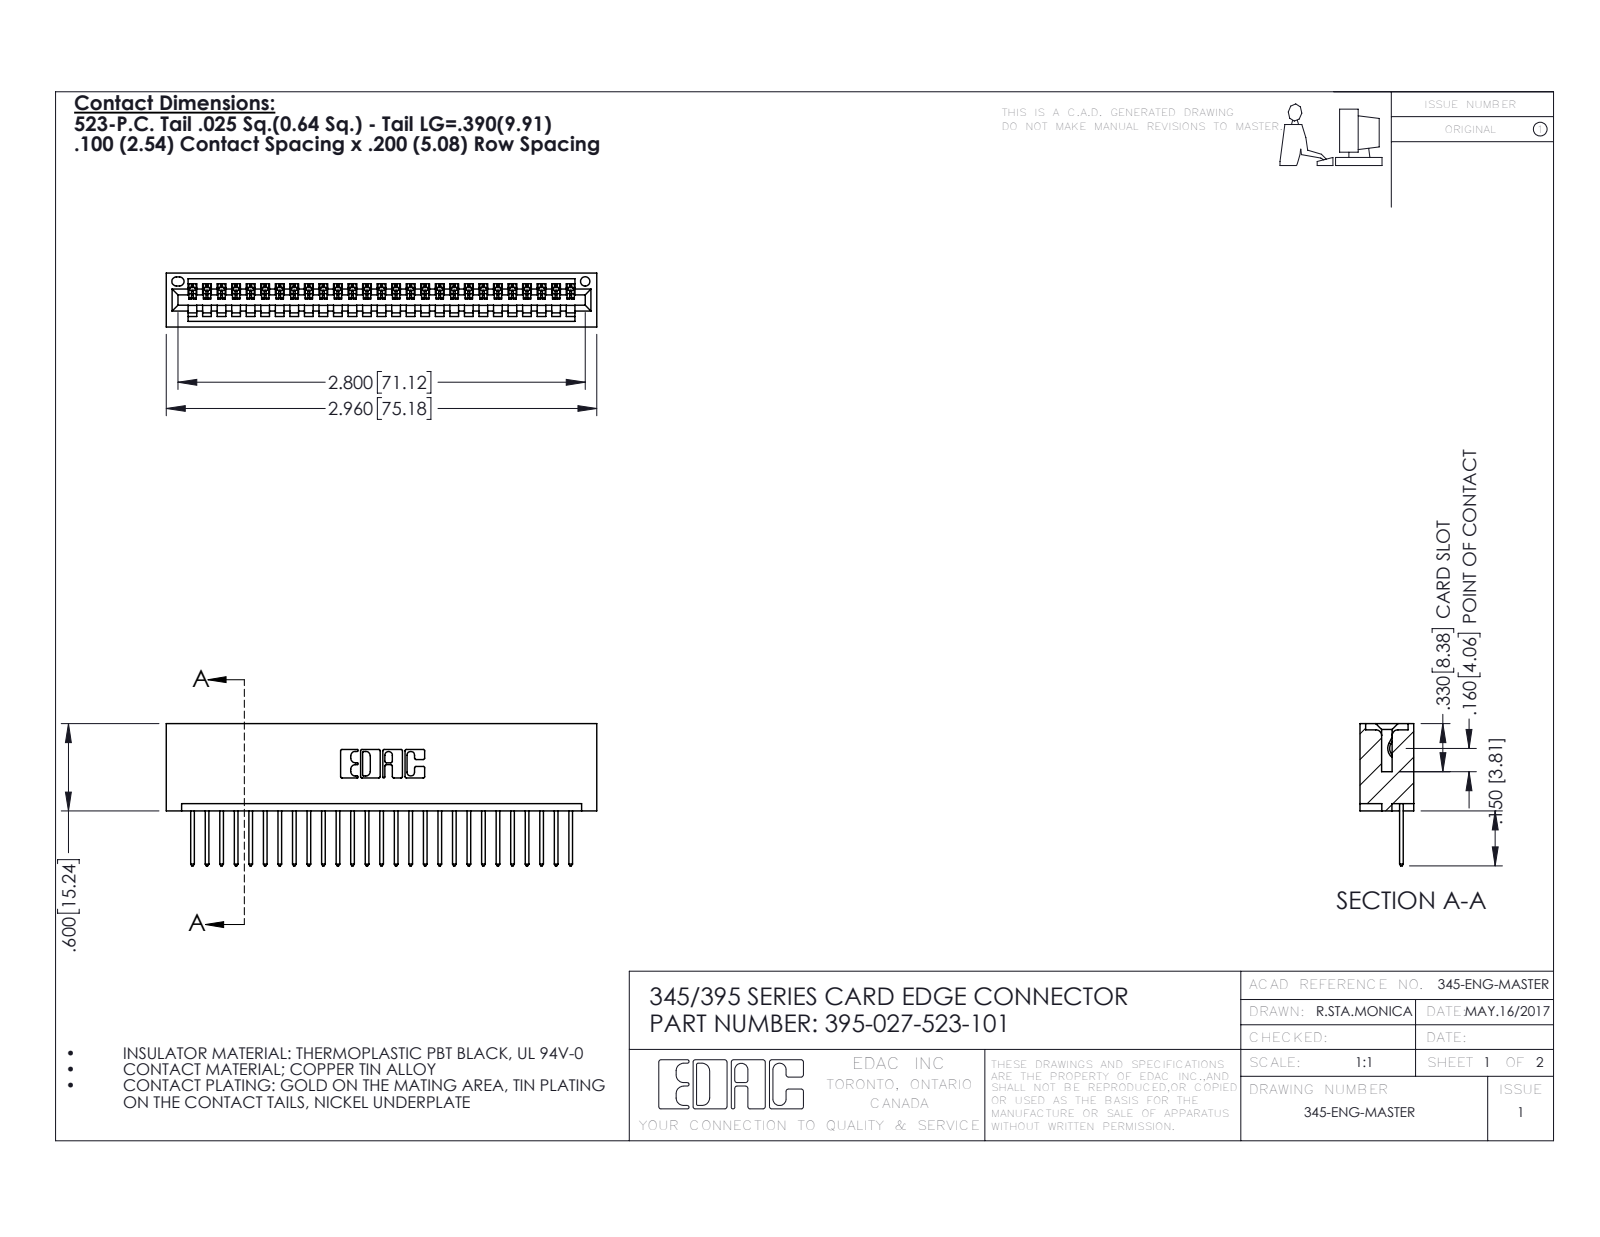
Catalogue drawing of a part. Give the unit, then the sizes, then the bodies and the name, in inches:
Units: inches
Overall size (bounding box): 2.96 × 0.977 × 0.37
Round holes (diameter × count): ⌀0.064 ×1
Partial cylindrical surfaces — rounded edges, fillets, slot ends (radius × count): R0.006 ×54, R0.01 ×54, R0.01 ×22, R0.007 ×6, R0.031 ×6, R0.026 ×3, R0.031 ×2, R0.04 ×2
Main face-to-face distances: 0.298, 0.072, 0.2, 0.37, 0.098, 0.272, 0.025, 0.225, 0.149, 0.072
Volume: 0.463 in³ · Surface area: 15.66 in²
Bodies: 28 solids, 1684 faces (1156 planar, 528 cylindrical, 0 other)
Part name (STEP PRODUCT): 345-292-001_345-293-123; 345 Part_No Mounting Lugs; 395-027-523-101
STEP written by: SolidWorks 2016 (CONFIG_CONTROL_DESIGN)
